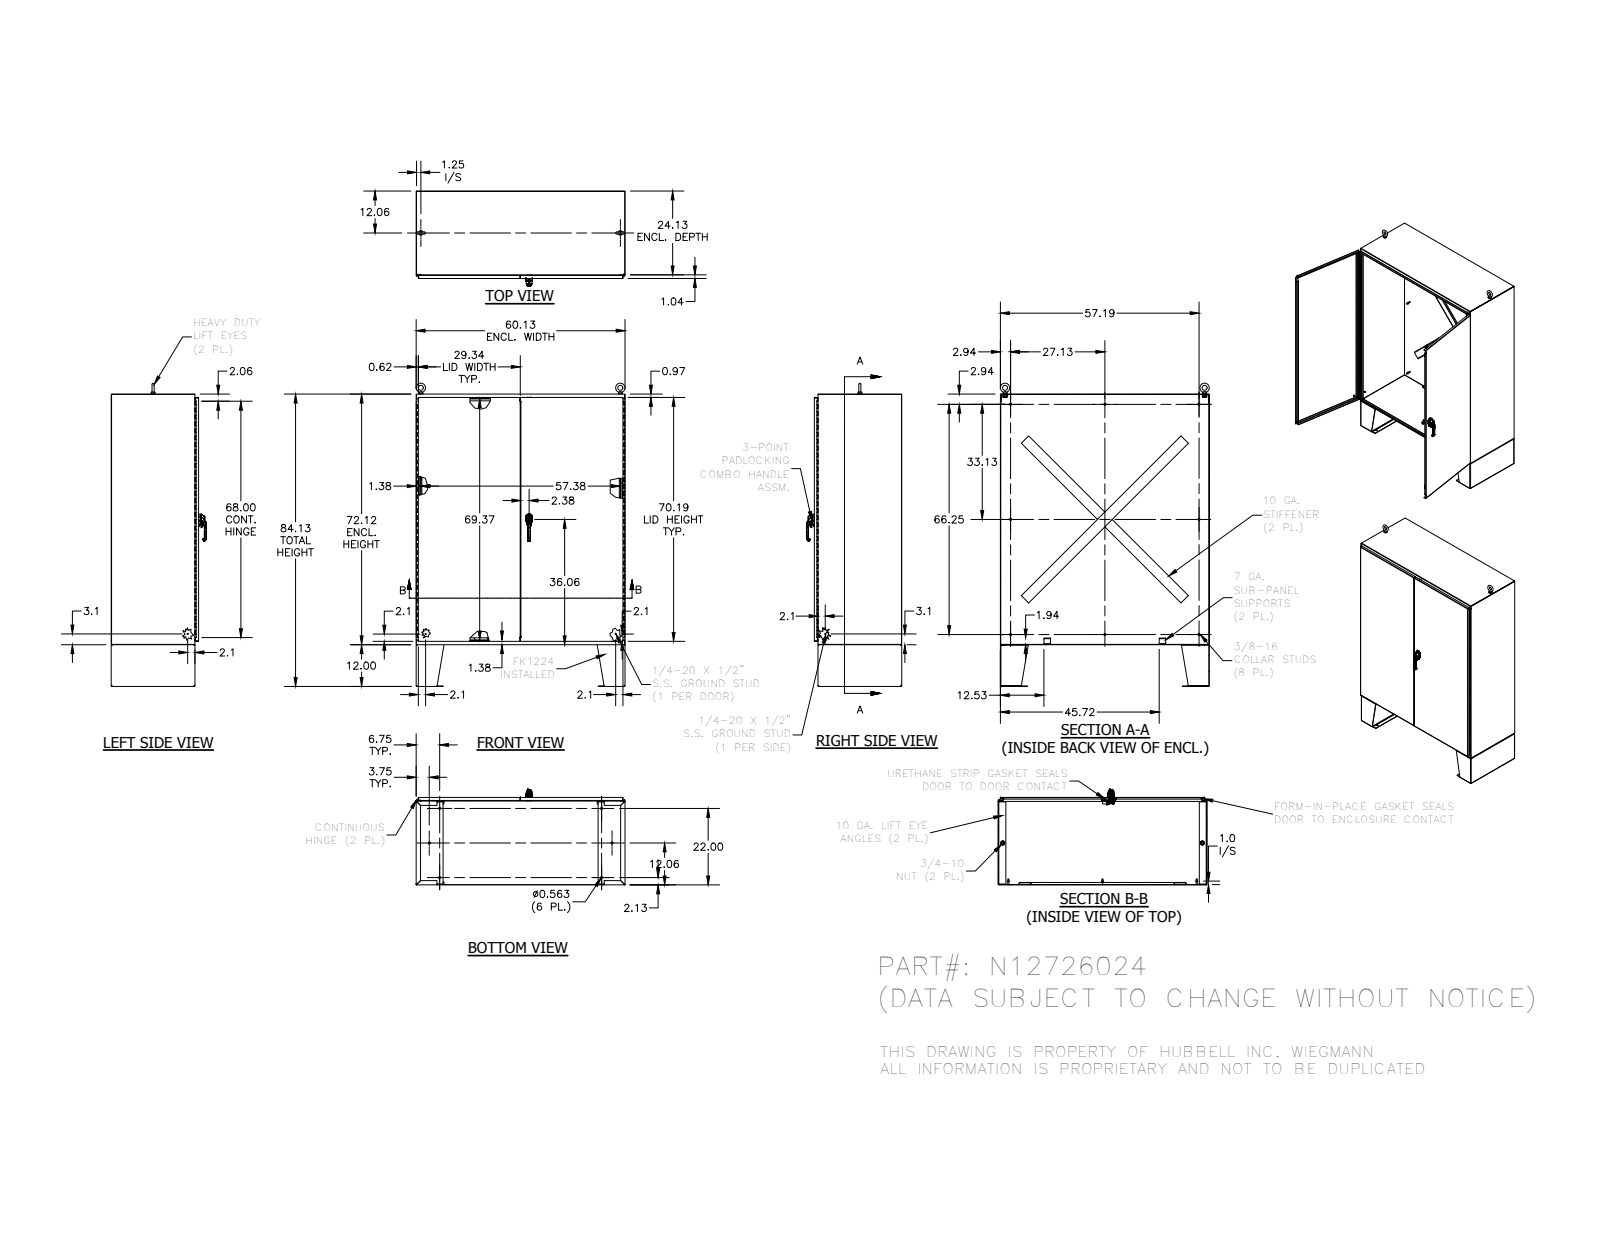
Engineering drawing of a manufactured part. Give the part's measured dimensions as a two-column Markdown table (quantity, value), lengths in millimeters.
| quantity | value |
| --- | --- |
| part name | N12726024 |
| STEP written by | SolidWorks 2018 (AUTOMOTIVE_DESIGN) |
| units | millimeters |
| bodies | 76 solids, 2596 faces (1528 planar, 768 cylindrical, 300 other) |
| overall size | 2216.1 × 1527.2 × 694.4 |
| volume | 30 530 000 mm³ |
| surface area | 24 300 000 mm² |
| round holes (diameter × count) | 14.3 × 18, 7 × 8, 5.1 × 4, 3.2 × 3, 7.1 × 3, 6.1 × 2, 6.4 × 2, 6.4 × 2, 10.2 × 2, 11.4 × 2, 16.3 × 2, 20.7 × 2 |
| round bosses / shafts (diameter × count) | 8.4 × 8, 15.9 × 5, 6.4 × 5, 15.9 × 3, 8.6 × 3, 31.8 × 2, 28.4 × 2, 25.4 × 2 |
| partial cylindrical surfaces (radius × count) | 0.8 × 24, 2.4 × 23, 5.6 × 22, 1.3 × 18, 0.6 × 16, 3.2 × 15, 0.8 × 13, 1.7 × 8 |
| main face-to-face distances | 2.4, 636.7, 634.3, 639.1, 1524.8, 1829.6, 1527.2, 1522.4, 1827.2, 1832 |
| hole center spacings | 51.8, 127, 287.4, 524.7, 577.9, 591.6, 1178.5, 1287 |
